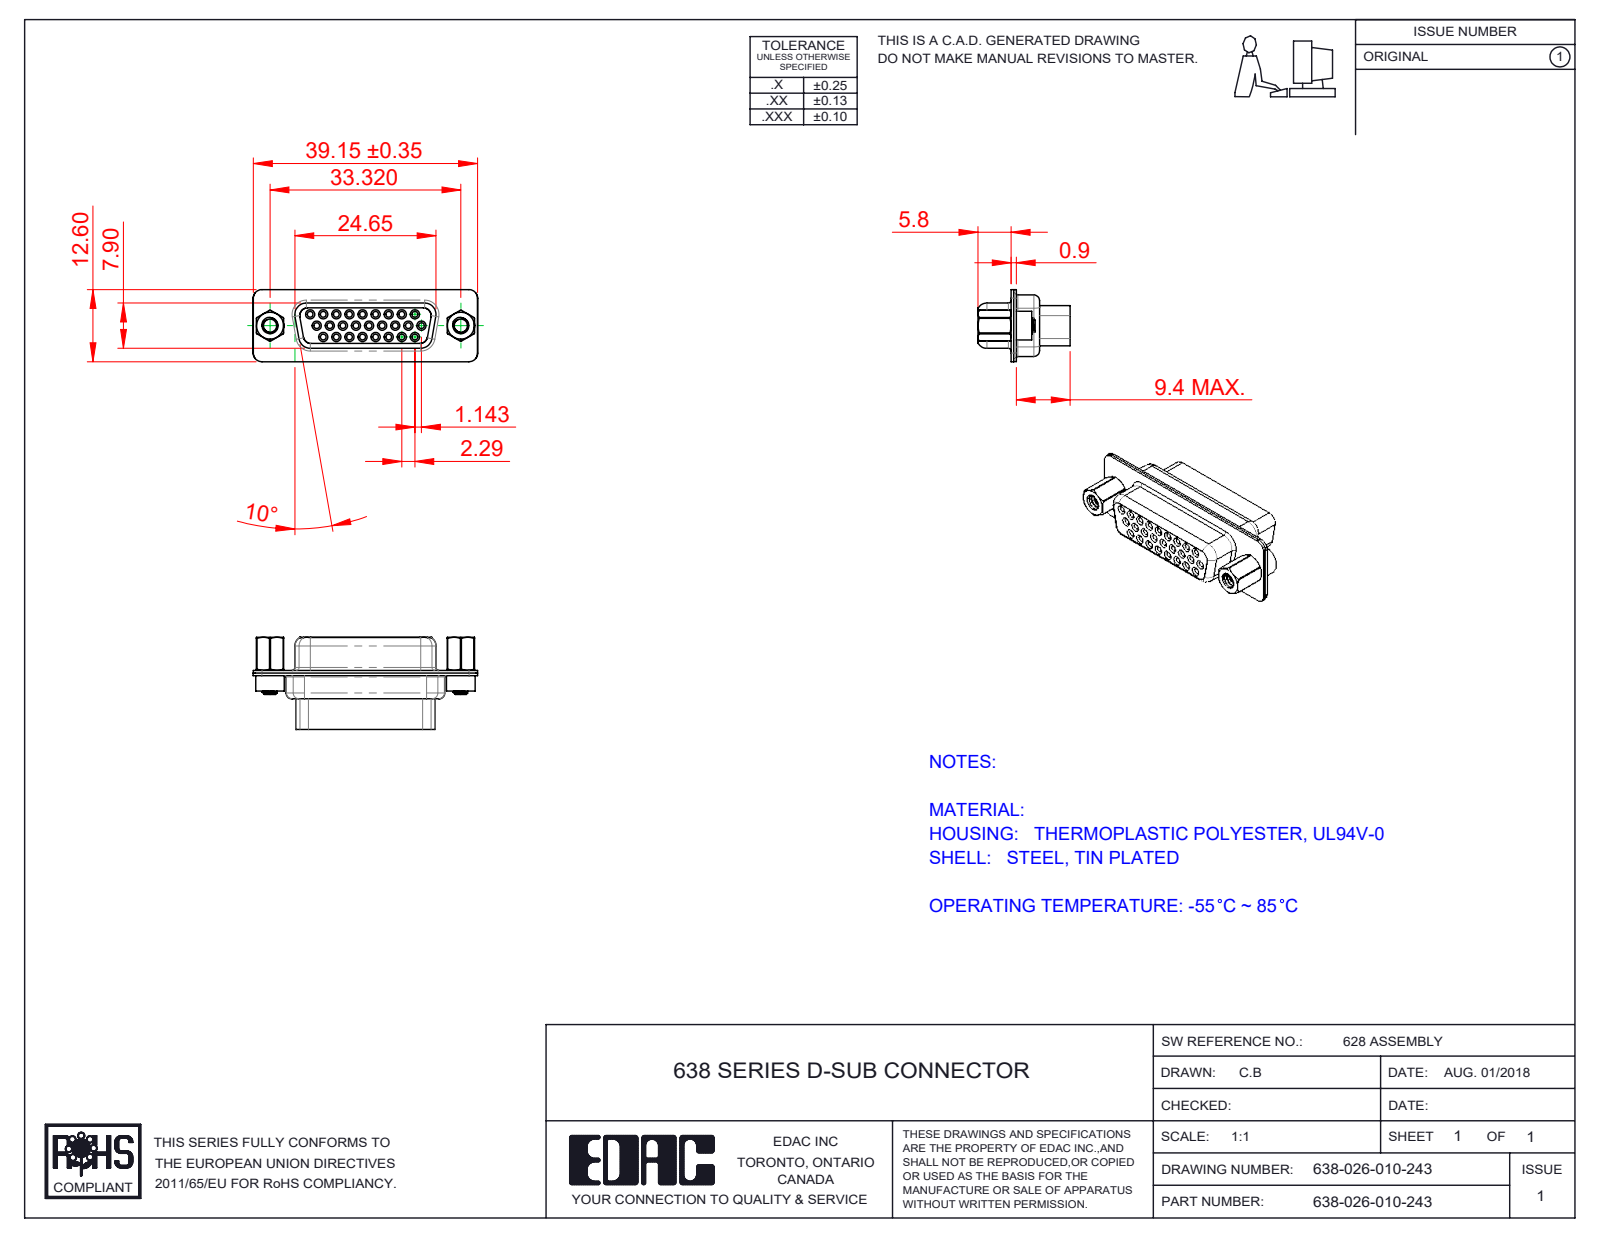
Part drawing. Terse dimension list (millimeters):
name: 638 Housing_26 Contacts HP; 638 Shell Front_26 Contacts; 638 4-40 Threaded Rivet; 638-026-010-243 (+2 more)
written by: SolidWorks 2020 (CONFIG_CONTROL_DESIGN)
unit: mm
bodies: 7 solids, 743 faces (167 planar, 417 cylindrical, 159 other)
size: 39.19 × 16.1 × 12.6
volume: 2 591 mm³; area: 6 922 mm²
holes: 26× ⌀1, 26× ⌀1.7, 26× ⌀1.8, 26× ⌀2, 2× ⌀2.26, 2× ⌀2.29, 2× ⌀4, 2× ⌀4.05, 2× ⌀4.85
bosses: 2× ⌀5, 2× ⌀4.95, 2× ⌀4.8, 2× ⌀2.79
rounds: 20× R1.5, 12× R2, 8× R1.55, 5× R1.35, 4× R0.25, 4× R0.5, 4× R0.55, 4× R0.7
face distances: 0.45, 0.4, 0.9, 6.6, 1.43, 8.88, 7, 9.4, 6.2, 0.85
hole spacings: 3.96, 2.28, 4.57, 6.05, 2.29, 8.24, 6.86, 10.48
